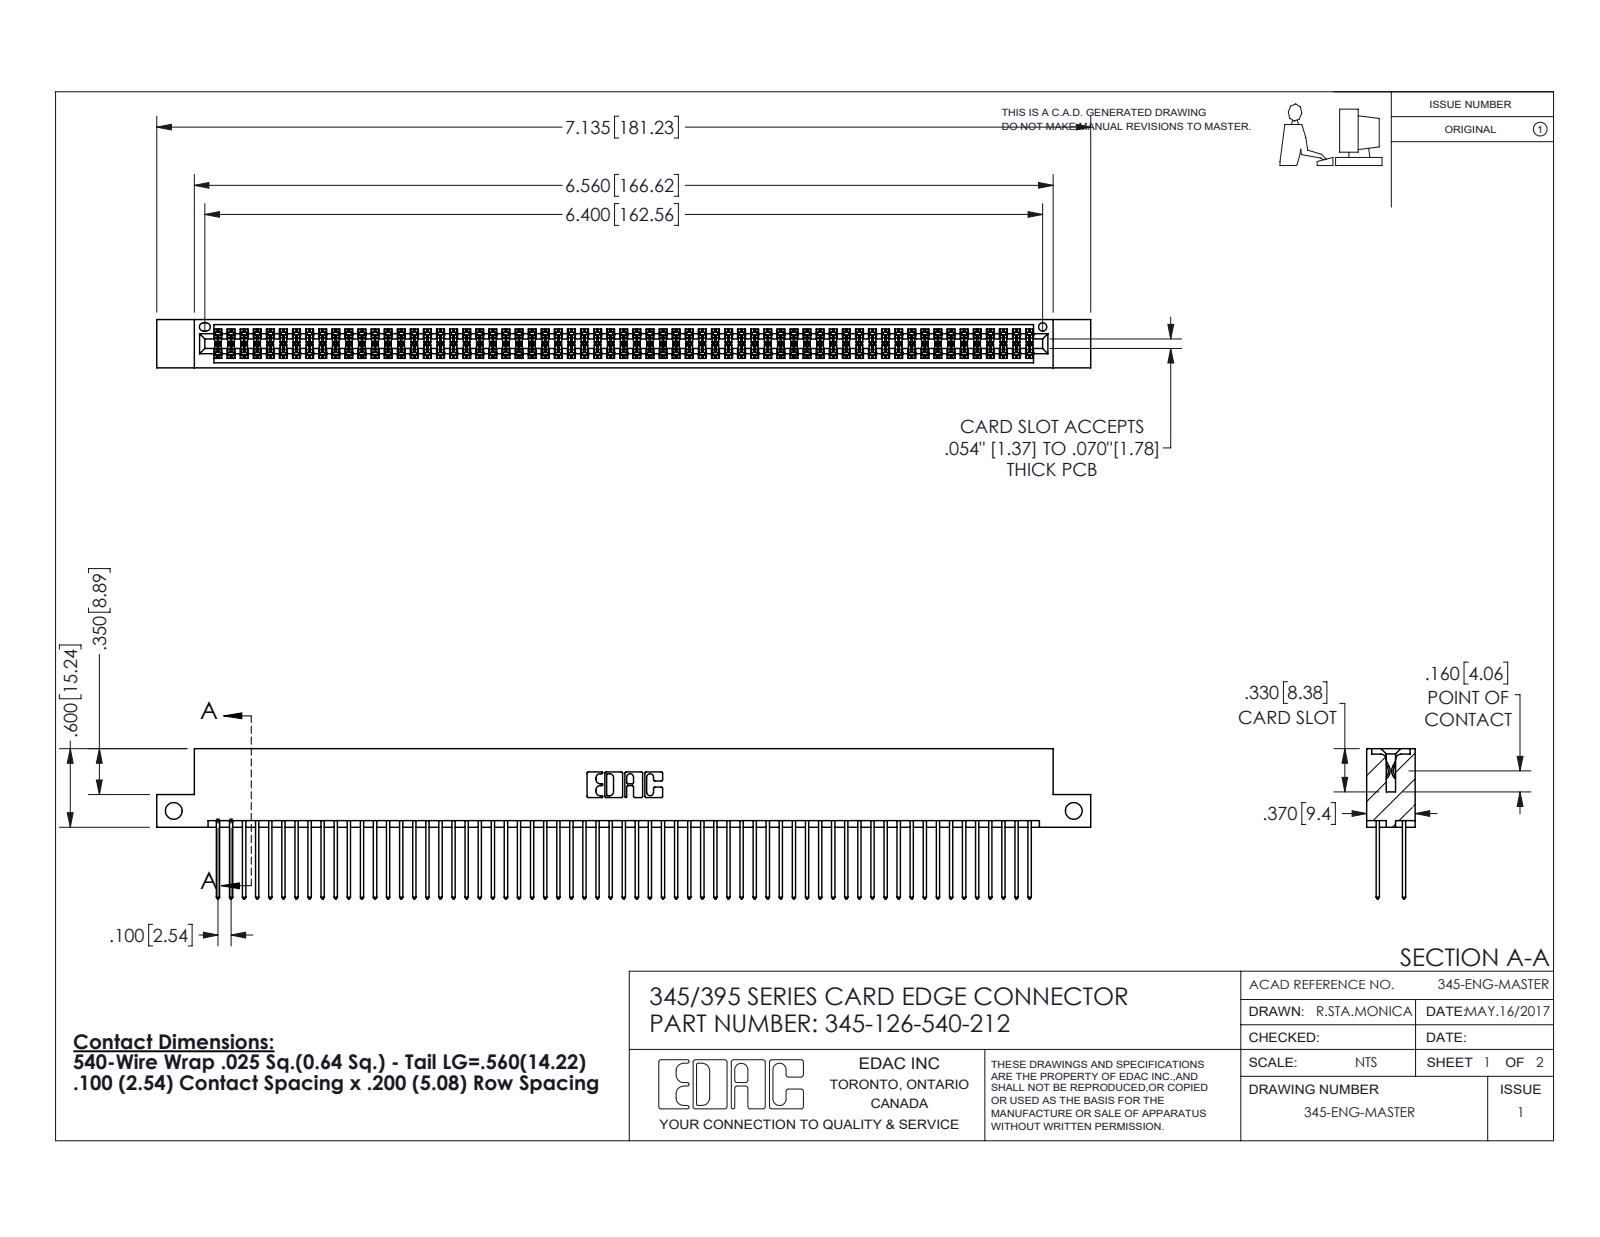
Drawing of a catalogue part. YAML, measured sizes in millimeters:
part_name: "345-126-540-212; 345-292-001_345-293-140; 345 Part_Flush Mounting Lugs - Side Mount"
step_written_by: "SolidWorks 2016 (CONFIG_CONTROL_DESIGN)"
units: millimeters
bodies: {solids: 127, faces: 6426, planar: 4238, cylindrical: 2188, other: 0}
overall_size: [181.2, 29.1, 9.4]
volume: 18190
surface_area: 29370
round_holes:
  - {diameter: 3.3, count: 2}
  - {diameter: 1.6, count: 1}
partial_cylinders:
  - {radius: 0.2, count: 189}
  - {radius: 0.3, count: 126}
  - {radius: 0.3, count: 22}
  - {radius: 0.2, count: 6}
  - {radius: 0.8, count: 6}
  - {radius: 0.7, count: 3}
  - {radius: 0.4, count: 2}
  - {radius: 0.5, count: 2}
face_to_face_distances: [7.6, 1.8, 5.1, 2.5, 6.9, 0.6, 5.7, 9.4, 4.4, 3.8]
hole_center_spacings: [174.6]
